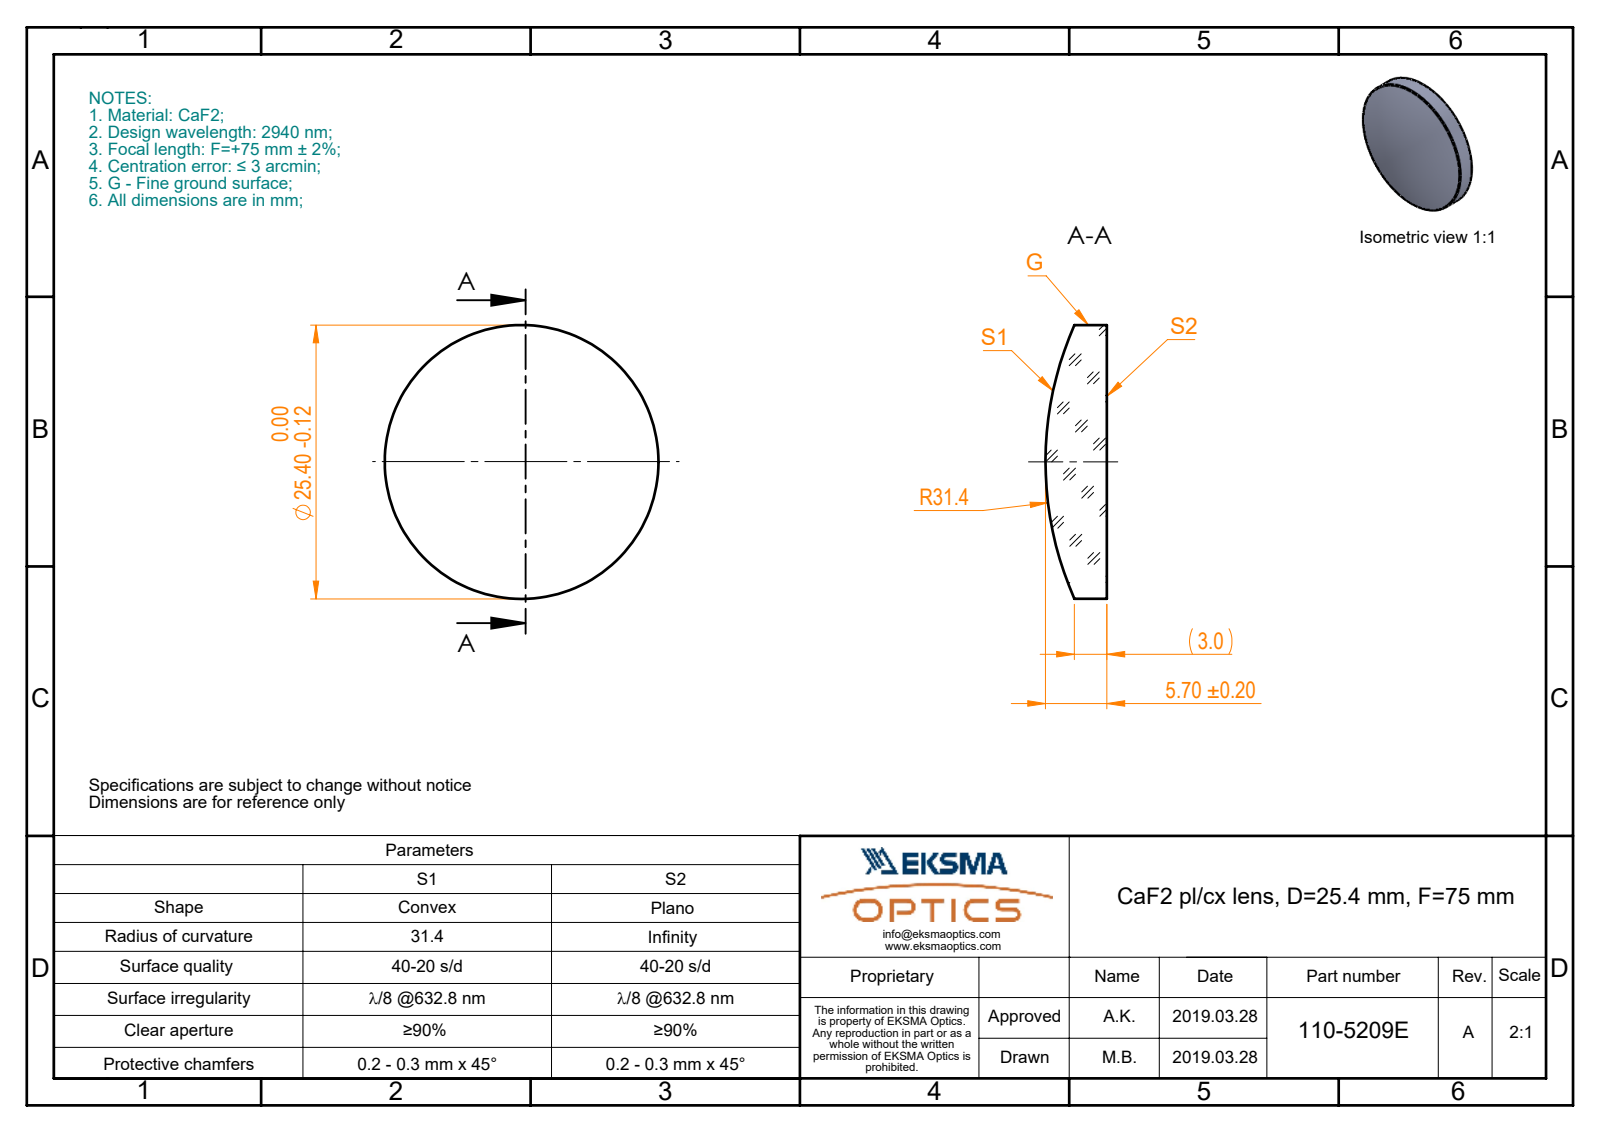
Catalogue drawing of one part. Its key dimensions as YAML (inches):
part_name: "110-5209E CaF2 pl-cx 25.4 F75"
step_written_by: "SolidWorks 2017 (CONFIG_CONTROL_DESIGN)"
units: inches
bodies: {solids: 1, faces: 5, planar: 1, cylindrical: 2, other: 2}
overall_size: [1, 1, 0.224]
volume: 0.135
surface_area: 1.979
round_bosses_or_shafts:
  - {diameter: 1, count: 1}
